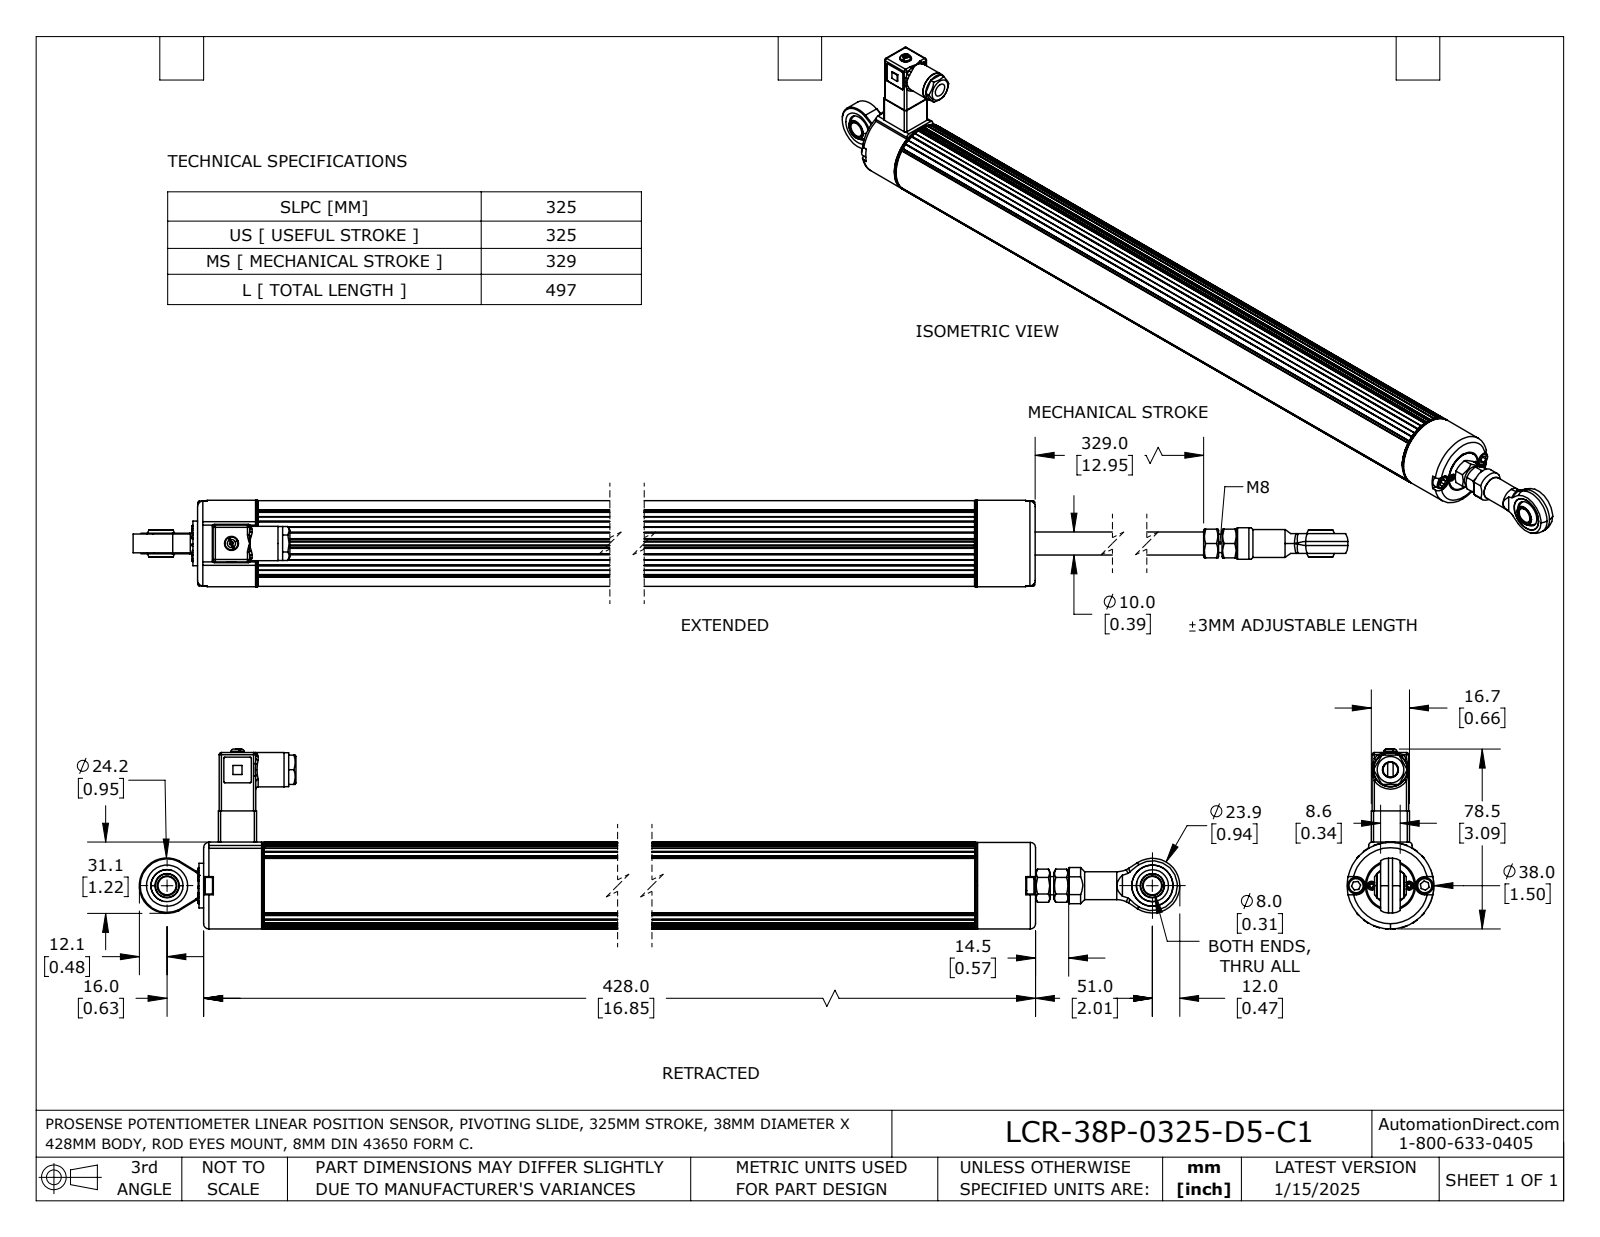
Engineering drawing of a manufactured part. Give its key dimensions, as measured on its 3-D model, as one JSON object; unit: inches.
{"part_name": "LCR-38P-0325-D5-C1", "step_written_by": "SolidWorks 2023 (AUTOMOTIVE_DESIGN)", "units": "inches", "bodies": {"solids": 11, "faces": 657, "planar": 295, "cylindrical": 210, "other": 152}, "overall_size": [20.435, 3.093, 1.488], "volume_in3": 29.95, "surface_area_in2": 136.9, "round_holes": [[0.102, 6], [0.091, 4], [0.315, 3], [0.551, 3], [0.094, 2], [0.1, 2], [0.111, 2], [0.134, 2], [0.152, 2], [0.165, 2], [0.079, 1], [0.118, 1]], "round_bosses_or_shafts": [[0.063, 6], [0.283, 4], [0.15, 4], [0.48, 2], [0.079, 2], [1.488, 1], [0.823, 1], [0.768, 1]], "partial_cylinders_radius": [[0.008, 32], [0.039, 20], [0.02, 12], [0.016, 6], [0.012, 2], [0.059, 2], [0.083, 2], [0.098, 2]], "face_to_face_distances": [14.764, 1.043, 15.807, 0.031, 0.045, 0.612, 0.598, 0.014, 0.644, 0.138], "hole_center_spacings": [0.632, 0.075, 0.634, 0.264, 0.268, 0.285, 0.323, 0.394]}
